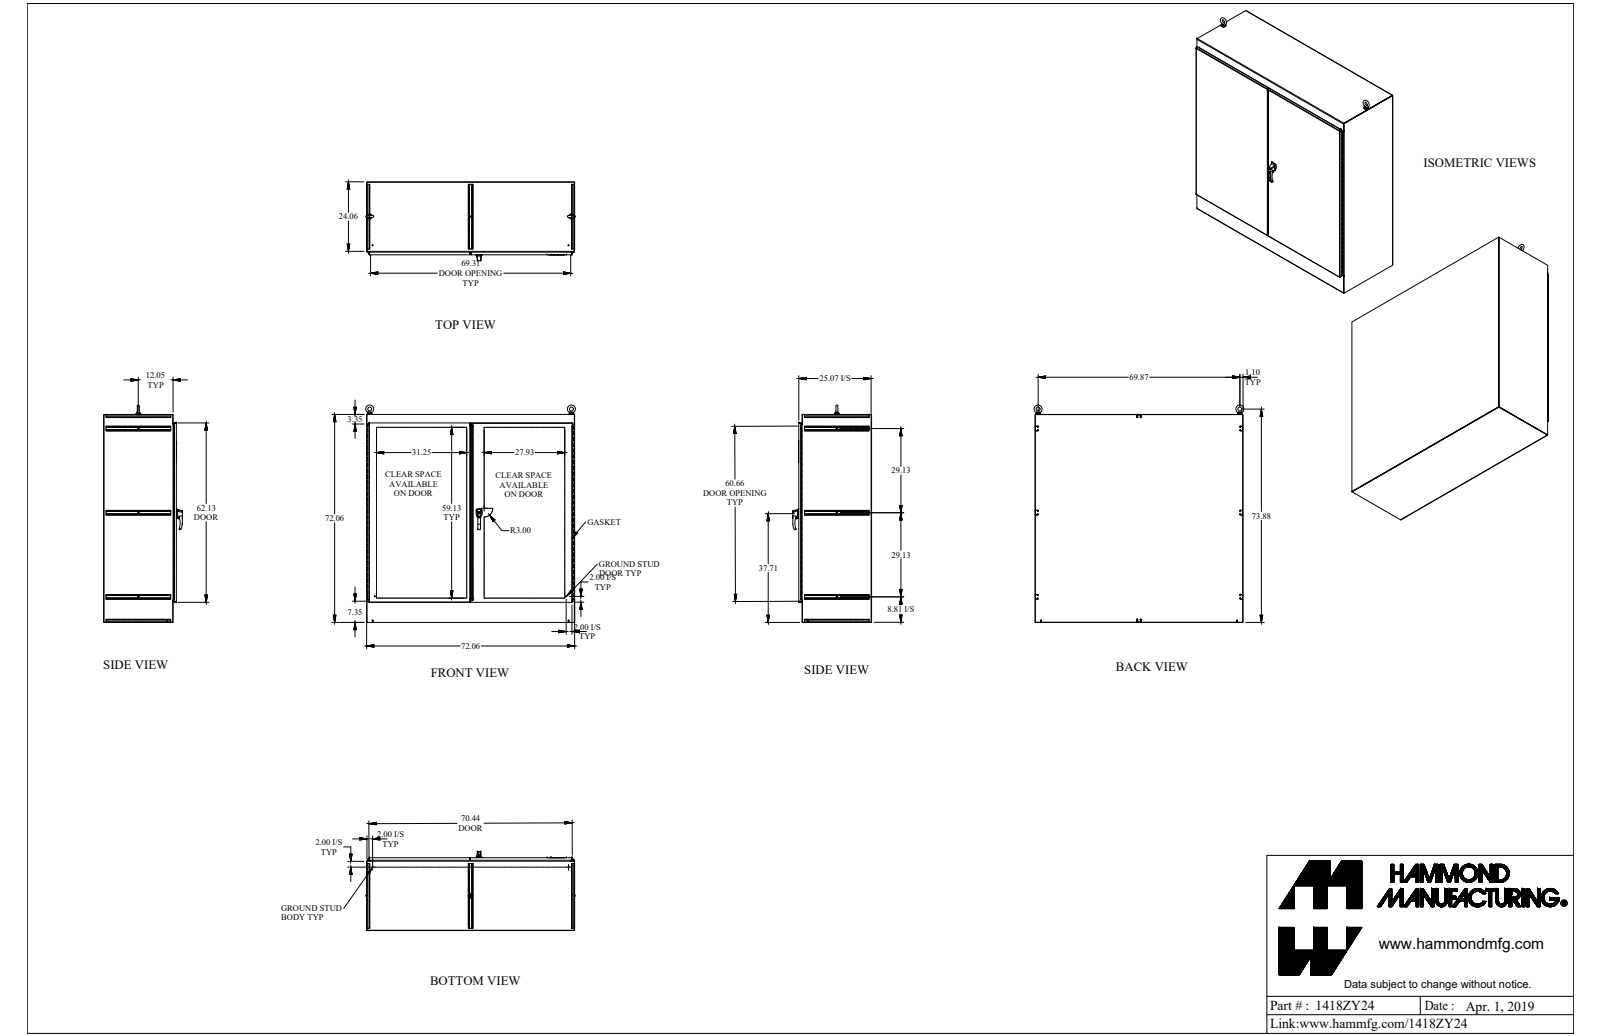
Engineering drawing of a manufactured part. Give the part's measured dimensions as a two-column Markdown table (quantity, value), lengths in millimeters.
| quantity | value |
| --- | --- |
| part name | 1418ZY24_Default |
| STEP written by | SolidWorks 2019 (CONFIG_CONTROL_DESIGN) |
| units | millimeters |
| bodies | 71 solids, 2583 faces (1198 planar, 1220 cylindrical, 165 other) |
| overall size | 1923.1 × 1857.2 × 694.4 |
| volume | 34 360 000 mm³ |
| surface area | 26 310 000 mm² |
| round holes (diameter × count) | 7.7 × 20, 12.7 × 4, 2.8 × 2, 6.4 × 2, 6.5 × 2, 7.1 × 2, 7.1 × 2, 8 × 2, 9.9 × 2, 10.5 × 2, 13.4 × 2, 15.9 × 2 |
| round bosses / shafts (diameter × count) | 7.1 × 6, 6.4 × 4, 44.5 × 2, 38.1 × 2, 31.8 × 2, 25.4 × 2, 19.1 × 2, 18.7 × 2 |
| partial cylindrical surfaces (radius × count) | 1.1 × 54, 3.5 × 48, 3.2 × 22, 1.2 × 20, 3.6 × 20, 0.5 × 16, 1.5 × 10, 1.3 × 8 |
| main face-to-face distances | 2.4, 1827.9, 3.2, 635.1, 638.2, 637.5, 640.6, 1825.5, 1830.3, 29.5 |
| hole center spacings | 152.4, 1792.8, 304.8, 1812.2, 457.2, 1843.9, 609.6, 1887.5 |
